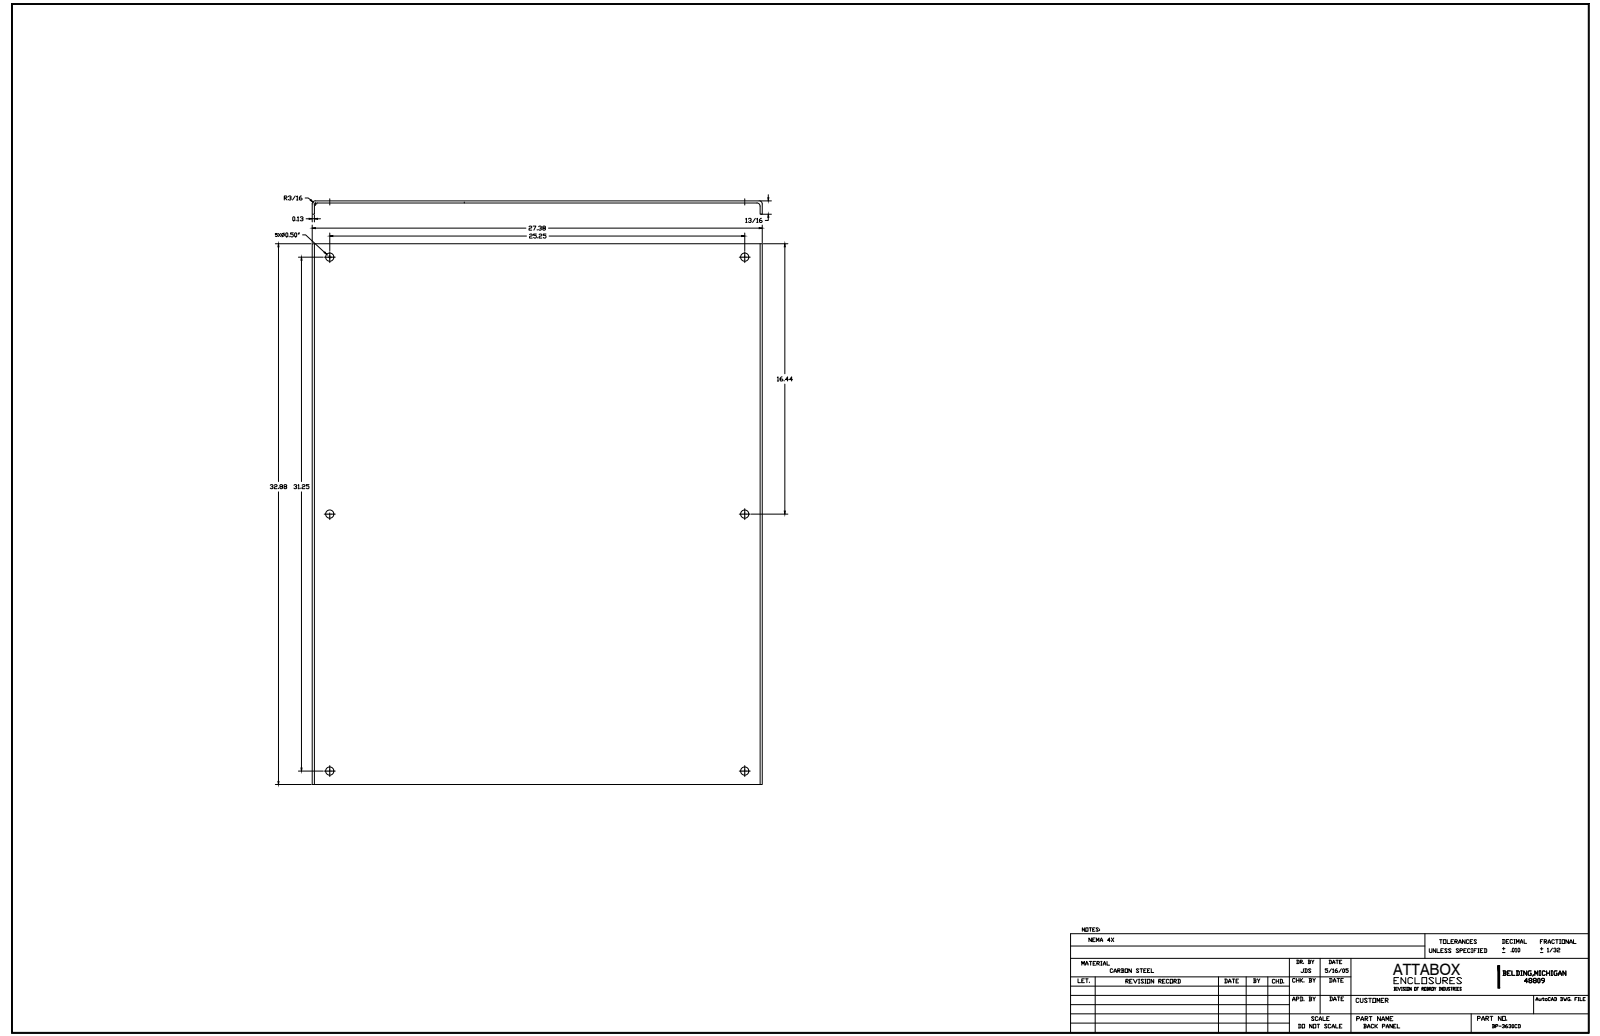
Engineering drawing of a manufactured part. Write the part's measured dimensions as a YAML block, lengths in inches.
part_name: "BP3630CD"
step_written_by: "SolidWorks 2018 (AUTOMOTIVE_DESIGN)"
units: inches
bodies: {solids: 1, faces: 20, planar: 10, cylindrical: 10, other: 0}
overall_size: [32.875, 27.375, 0.813]
volume: 126.9
surface_area: 1897
round_holes:
  - {diameter: 0.5, count: 6}
partial_cylinders:
  - {radius: 0.063, count: 2}
  - {radius: 0.188, count: 2}
face_to_face_distances: [0.135, 0.135, 27.24, 27.375, 27.105, 0.678, 0.812, 32.875]
hole_center_spacings: [15.625, 29.693, 25.25, 31.25, 40.176]
